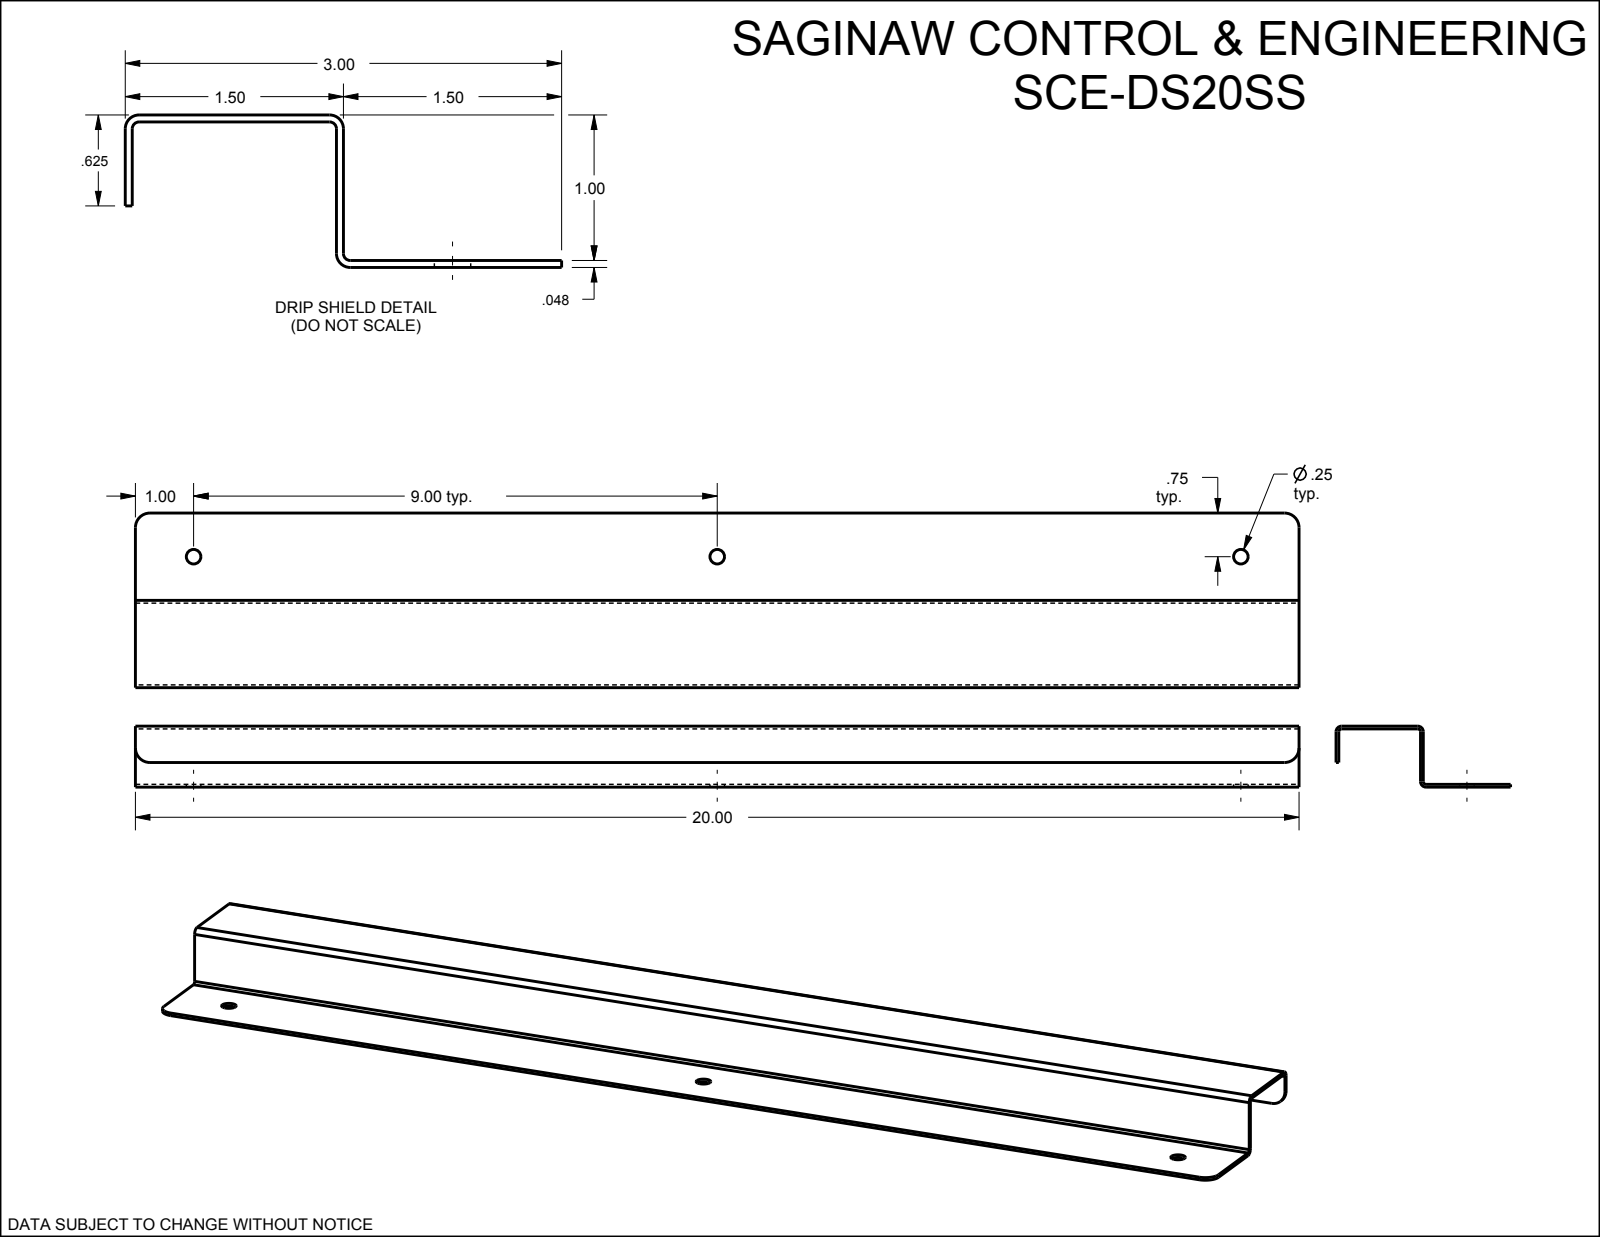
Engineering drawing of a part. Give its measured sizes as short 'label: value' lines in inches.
name: SCE-DS20SS
written by: SolidWorks 2019 (CONFIG_CONTROL_DESIGN)
unit: in
bodies: 1 solid, 25 faces (12 planar, 13 cylindrical, 0 other)
size: 20 × 3 × 1.048
volume: 4.297 in³; area: 181.5 in²
holes: 3× ⌀0.25
rounds: 4× R0.25, 3× R0.047, 3× R0.095
face distances: 0.048, 1, 0.952, 1.048, 1.452, 1.5, 1.404, 0.423, 0.375, 0.577
hole spacings: 9, 18
